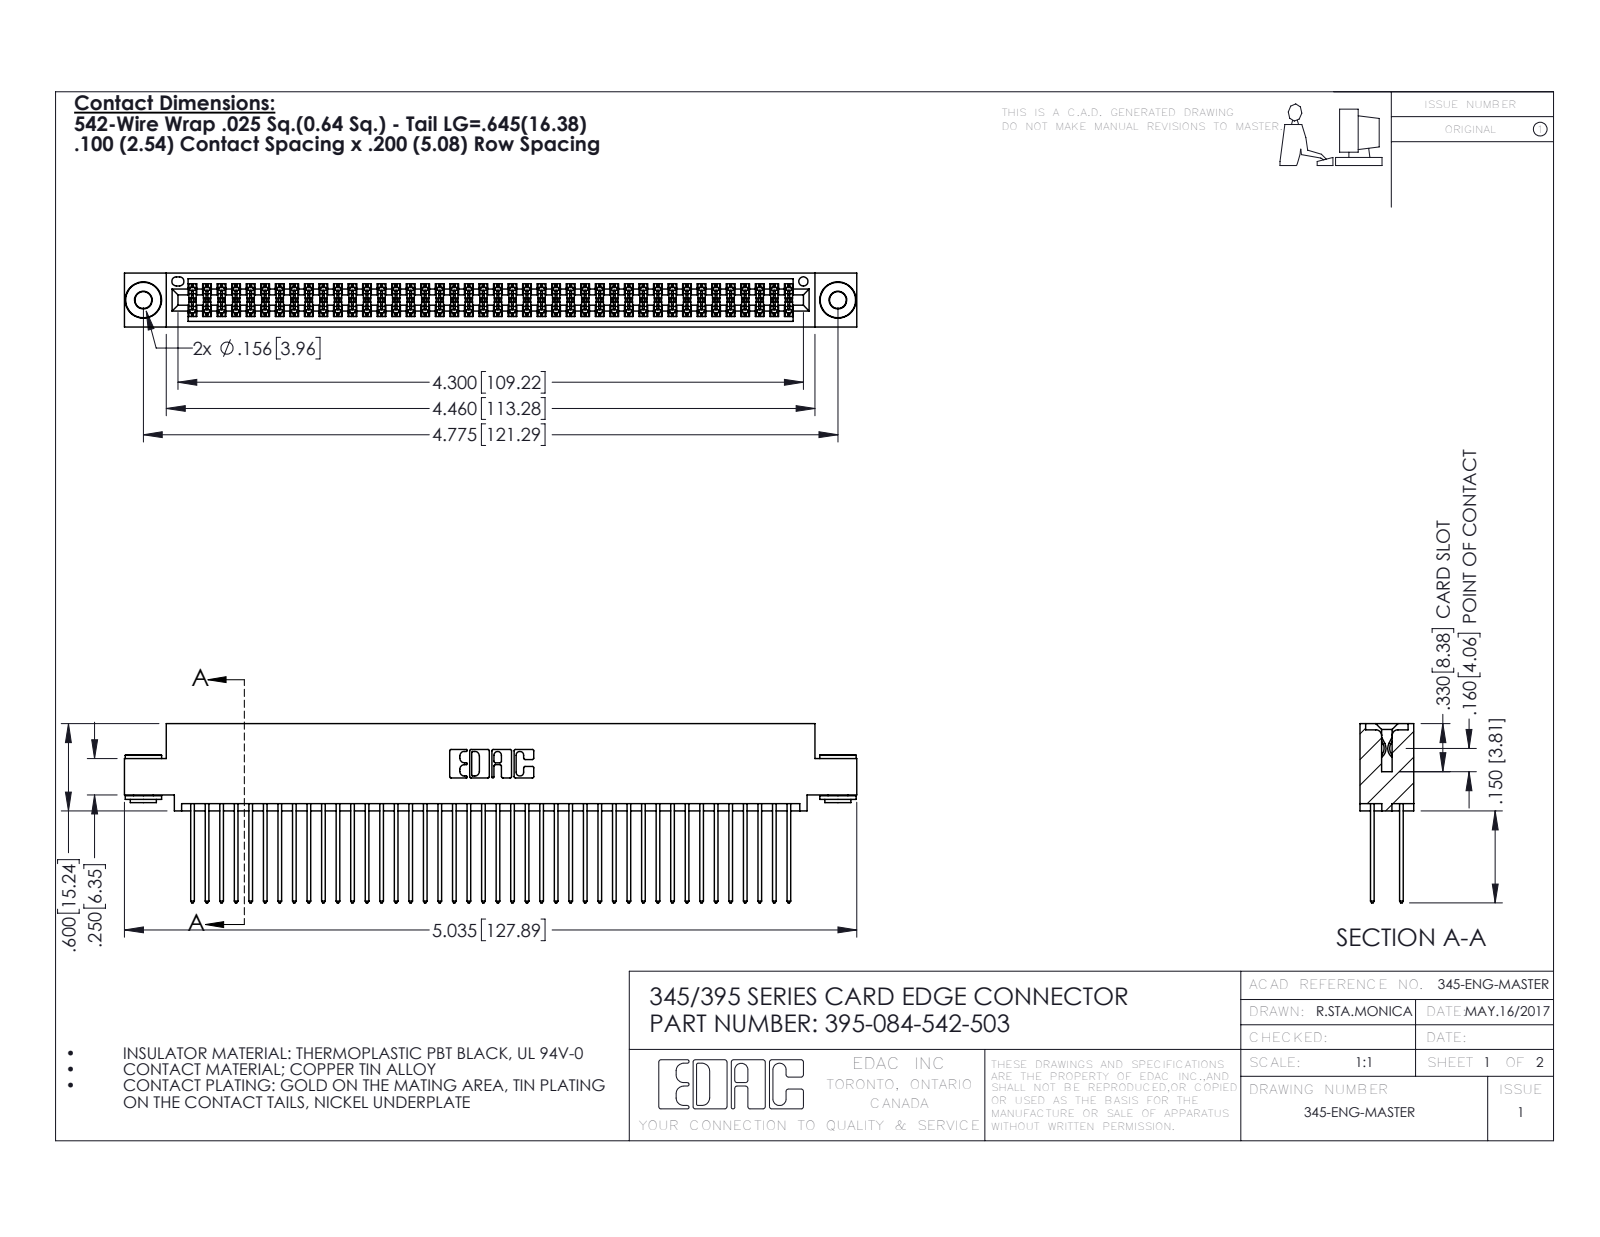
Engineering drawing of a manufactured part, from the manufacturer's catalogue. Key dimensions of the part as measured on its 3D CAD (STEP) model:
Part name (STEP PRODUCT): 395-084-542-503; 345-292-001_345-293-142; 345-250-002_345-250-002-102; 345 Part_0.110 Offset - 0.156 Dia-TH
STEP written by: SolidWorks 2016 (CONFIG_CONTROL_DESIGN)
Units: inches
Bodies: 87 solids, 4368 faces (2866 planar, 1494 cylindrical, 8 other)
Overall size (bounding box): 5.035 × 1.232 × 0.37
Volume: 0.779 in³ · Surface area: 32.54 in²
Round holes (diameter × count): ⌀0.116 ×2, ⌀0.156 ×2, ⌀0.064 ×1
Round bosses / shafts (diameter × count): ⌀0.25 ×2, ⌀0.18 ×2, ⌀0.136 ×2
Partial cylindrical surfaces — rounded edges, fillets, slot ends (radius × count): R0.006 ×126, R0.01 ×84, R0.01 ×22, R0.007 ×6, R0.031 ×6, R0.026 ×3, R0.014 ×2, R0.019 ×2
Main face-to-face distances: 0.072, 0.298, 0.2, 0.025, 0.098, 0.272, 0.225, 0.37, 0.175, 0.149
Hole centre spacings: 0.27, 4.539, 4.775
